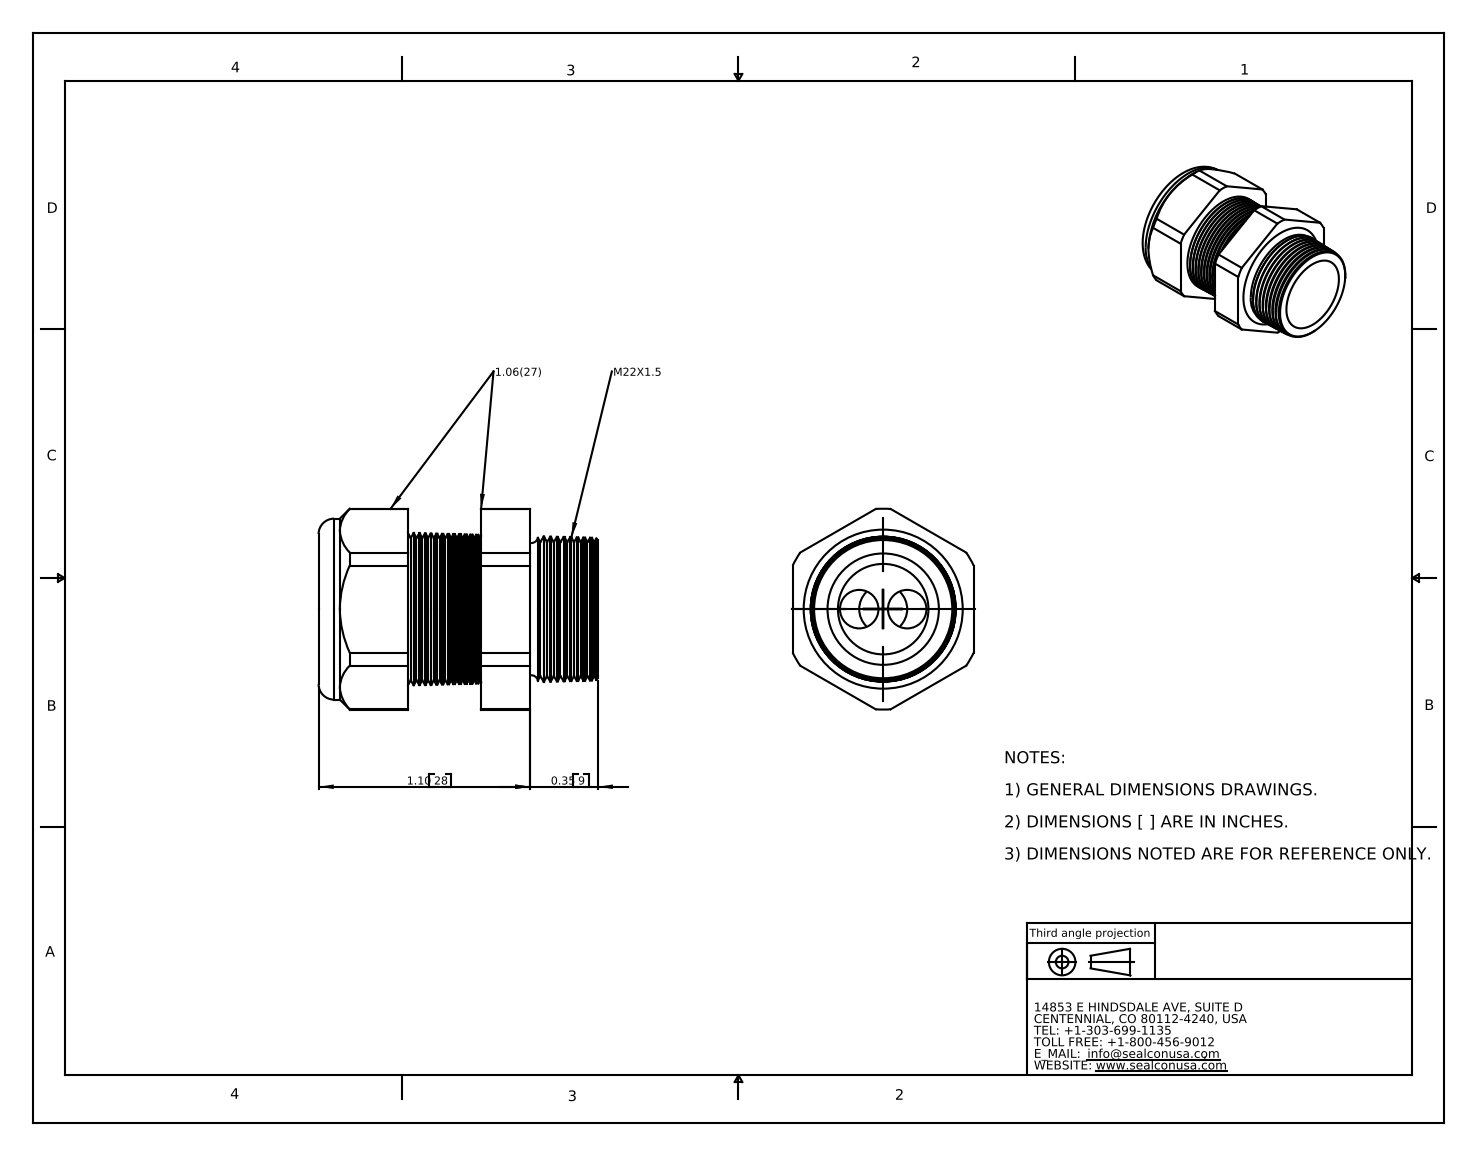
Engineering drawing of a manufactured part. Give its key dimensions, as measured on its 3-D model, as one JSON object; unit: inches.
{"part_name": "CD22M6-BK", "step_written_by": "SolidWorks 2007 (CONFIG_CONTROL_DESIGN)", "units": "inches", "bodies": {"solids": 2, "faces": 190, "planar": 20, "cylindrical": 24, "other": 146}, "overall_size": [1.45, 1.043, 0.94], "volume_in3": 0.58, "surface_area_in2": 10.18, "round_holes": [[0.2, 2], [0.45, 1], [0.47, 1]], "round_bosses_or_shafts": [[0.94, 1]], "partial_cylinders_radius": [[0.522, 1]], "face_to_face_distances": [0.94, 0.844, 0.465, 0.38, 1.1, 0.635, 0.256, 1.45, 0.985, 0.606], "hole_center_spacings": [0.124, 0.249]}
